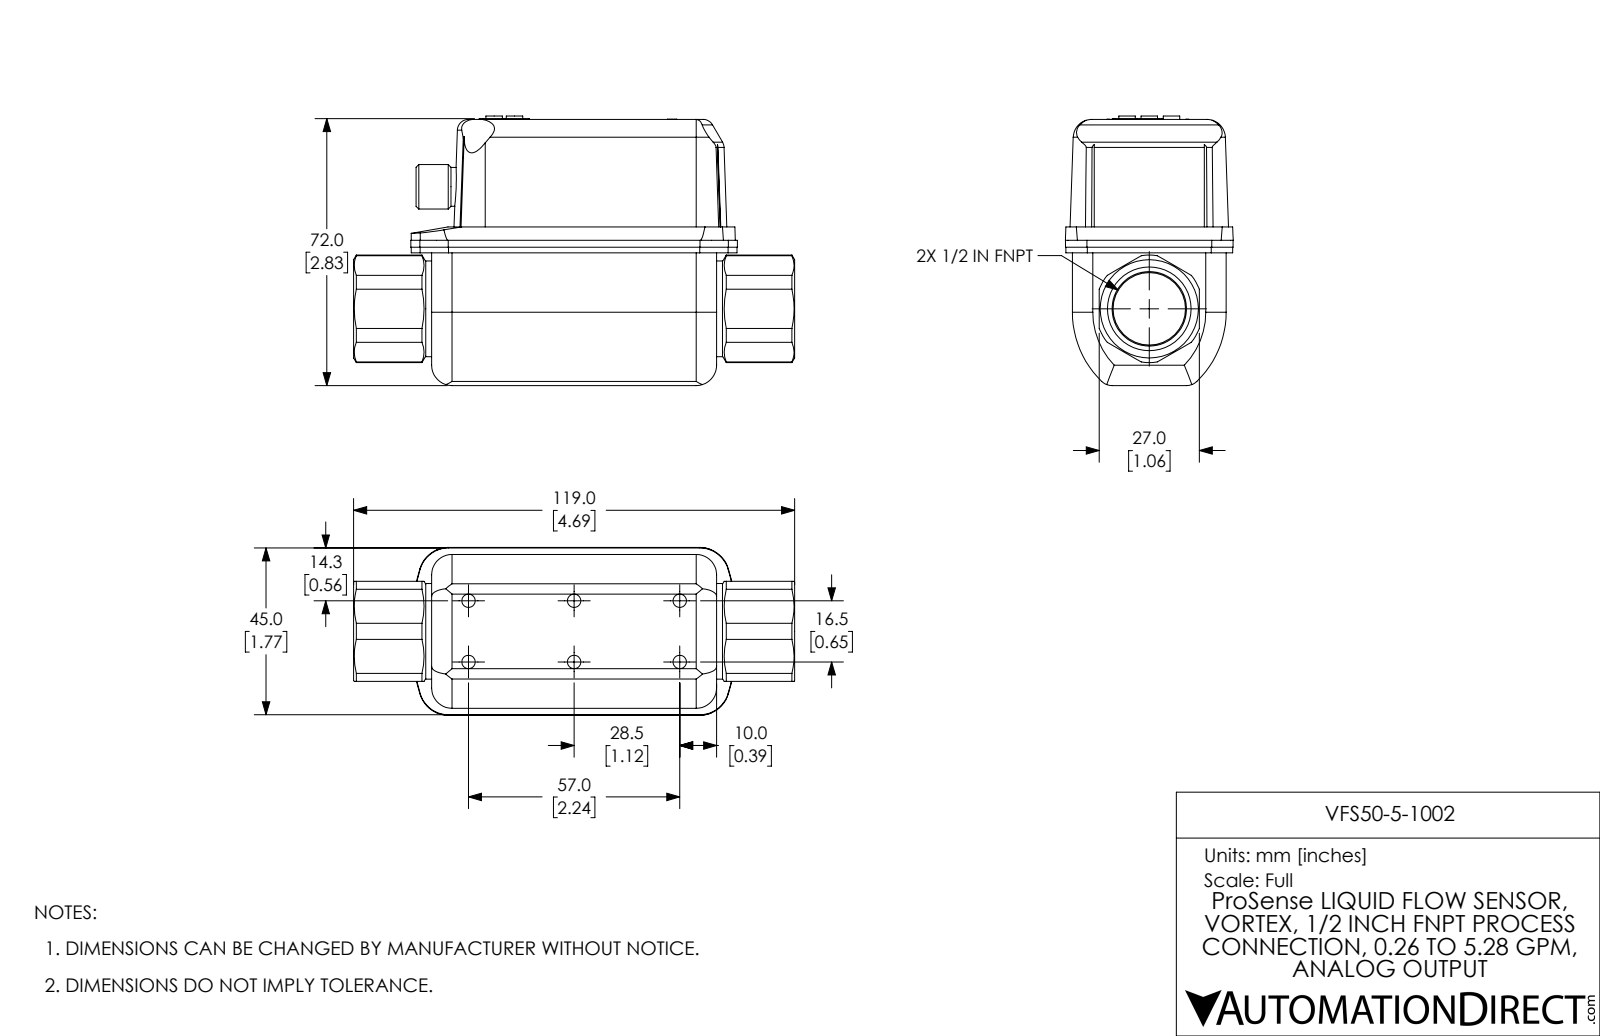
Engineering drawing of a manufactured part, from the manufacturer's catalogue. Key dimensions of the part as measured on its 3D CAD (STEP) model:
Part name (STEP PRODUCT): VFS50-5-1002
STEP written by: SolidWorks 2017 (AUTOMOTIVE_DESIGN)
Units: millimetres
Bodies: 1 solid, 219 faces (84 planar, 80 cylindrical, 55 other)
Overall size (bounding box): 119 × 72.7 × 45.29
Volume: 234 166 mm³ · Surface area: 27 599 mm²
Round holes (diameter × count): ⌀3.6 ×6, ⌀8.4 ×1
Round bosses / shafts (diameter × count): ⌀4.45 ×3, ⌀25.8 ×1, ⌀12 ×1, ⌀10.5 ×1
Partial cylindrical surfaces — rounded edges, fillets, slot ends (radius × count): R8 ×12, R5.5 ×6, R4 ×4, R60 ×4, R3.5 ×2, R5 ×2, R26 ×2, R0.6 ×1
Main face-to-face distances: 27, 71.8, 41.5, 36, 7.25, 34.25, 71.75, 35.8, 35.95, 11.05
Hole centre spacings: 28.5, 32.93, 16.5, 57, 59.34
